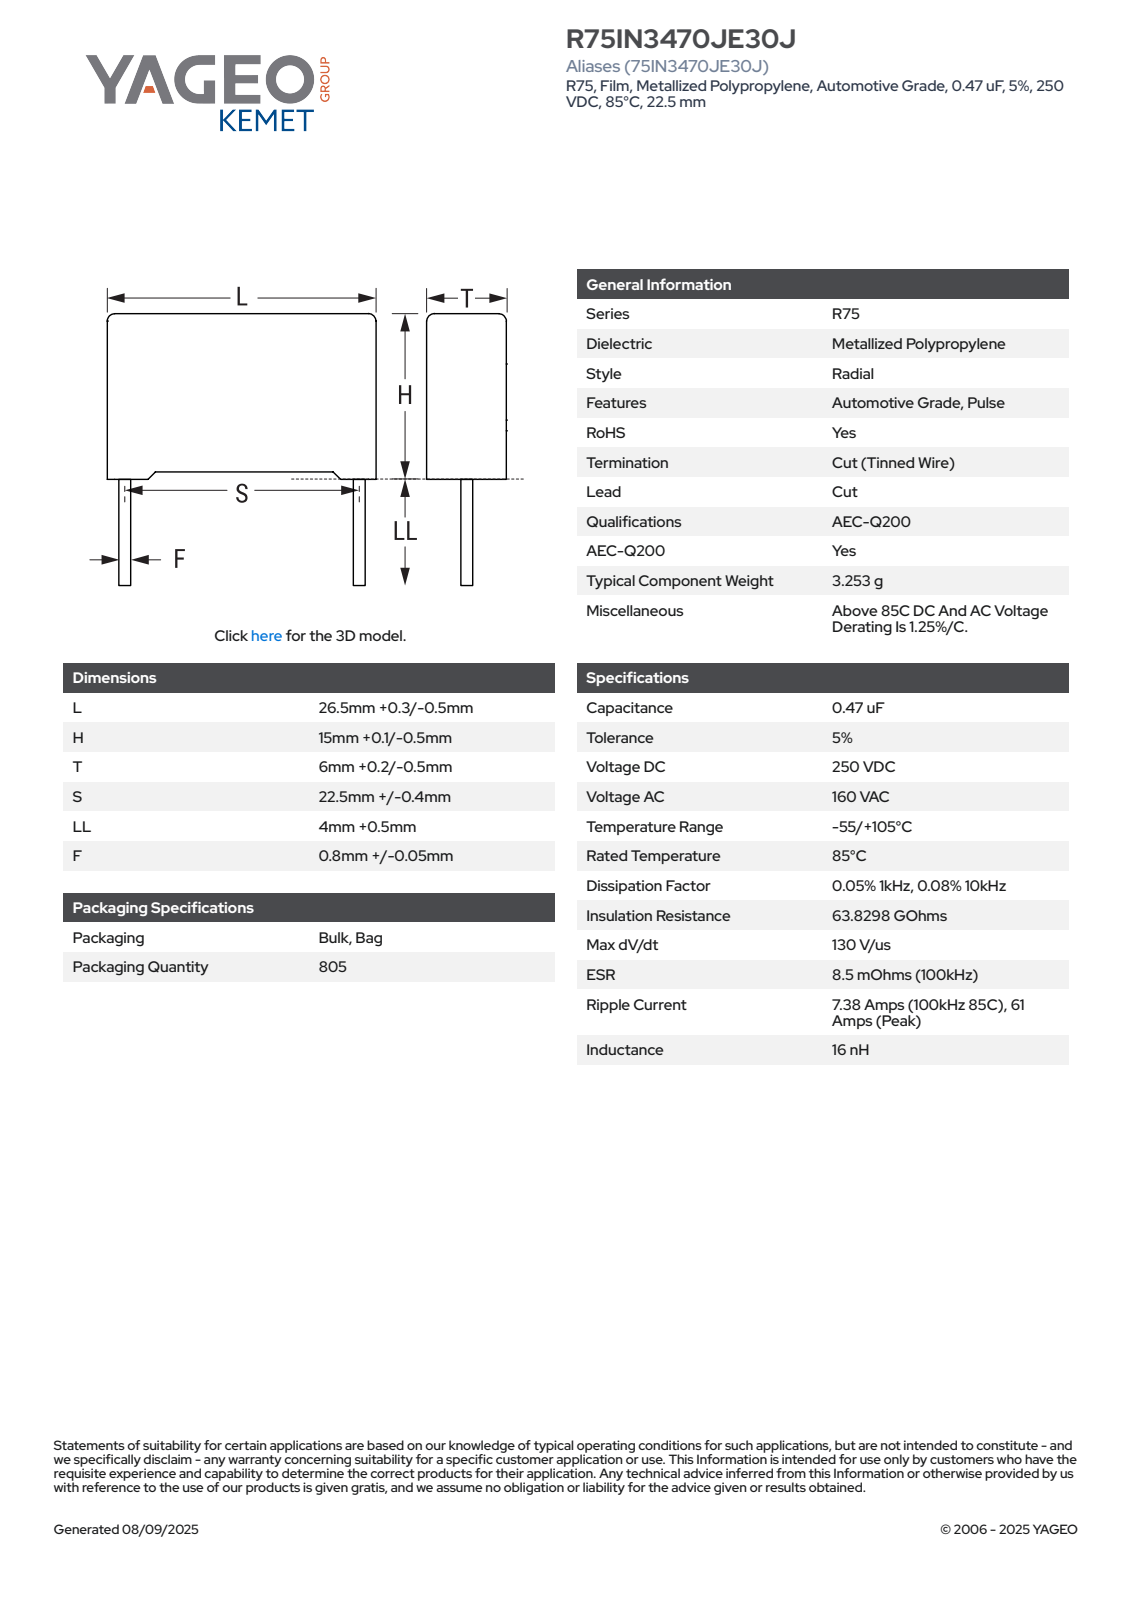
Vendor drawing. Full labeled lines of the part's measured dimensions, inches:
Part name (STEP PRODUCT): CFR_RB2_26.5X15X6_L26.8H15.1T6.2S22.5LL4.5F0.85
STEP written by: SolidWorks 2021 (AUTOMOTIVE_DESIGN)
Units: inches
Bodies: 4 solids, 85 faces (77 planar, 8 cylindrical, 0 other)
Overall size (bounding box): 1.055 × 0.772 × 0.244
Volume: 0.147 in³ · Surface area: 2.173 in²
Round bosses / shafts (diameter × count): ⌀0.033 ×2
Partial cylindrical surfaces — rounded edges, fillets, slot ends (radius × count): R0.02 ×4
Main face-to-face distances: 0.244, 0.565, 1.055, 0.574, 0.035, 0.02, 0.03, 0.594, 0.209, 0.174
